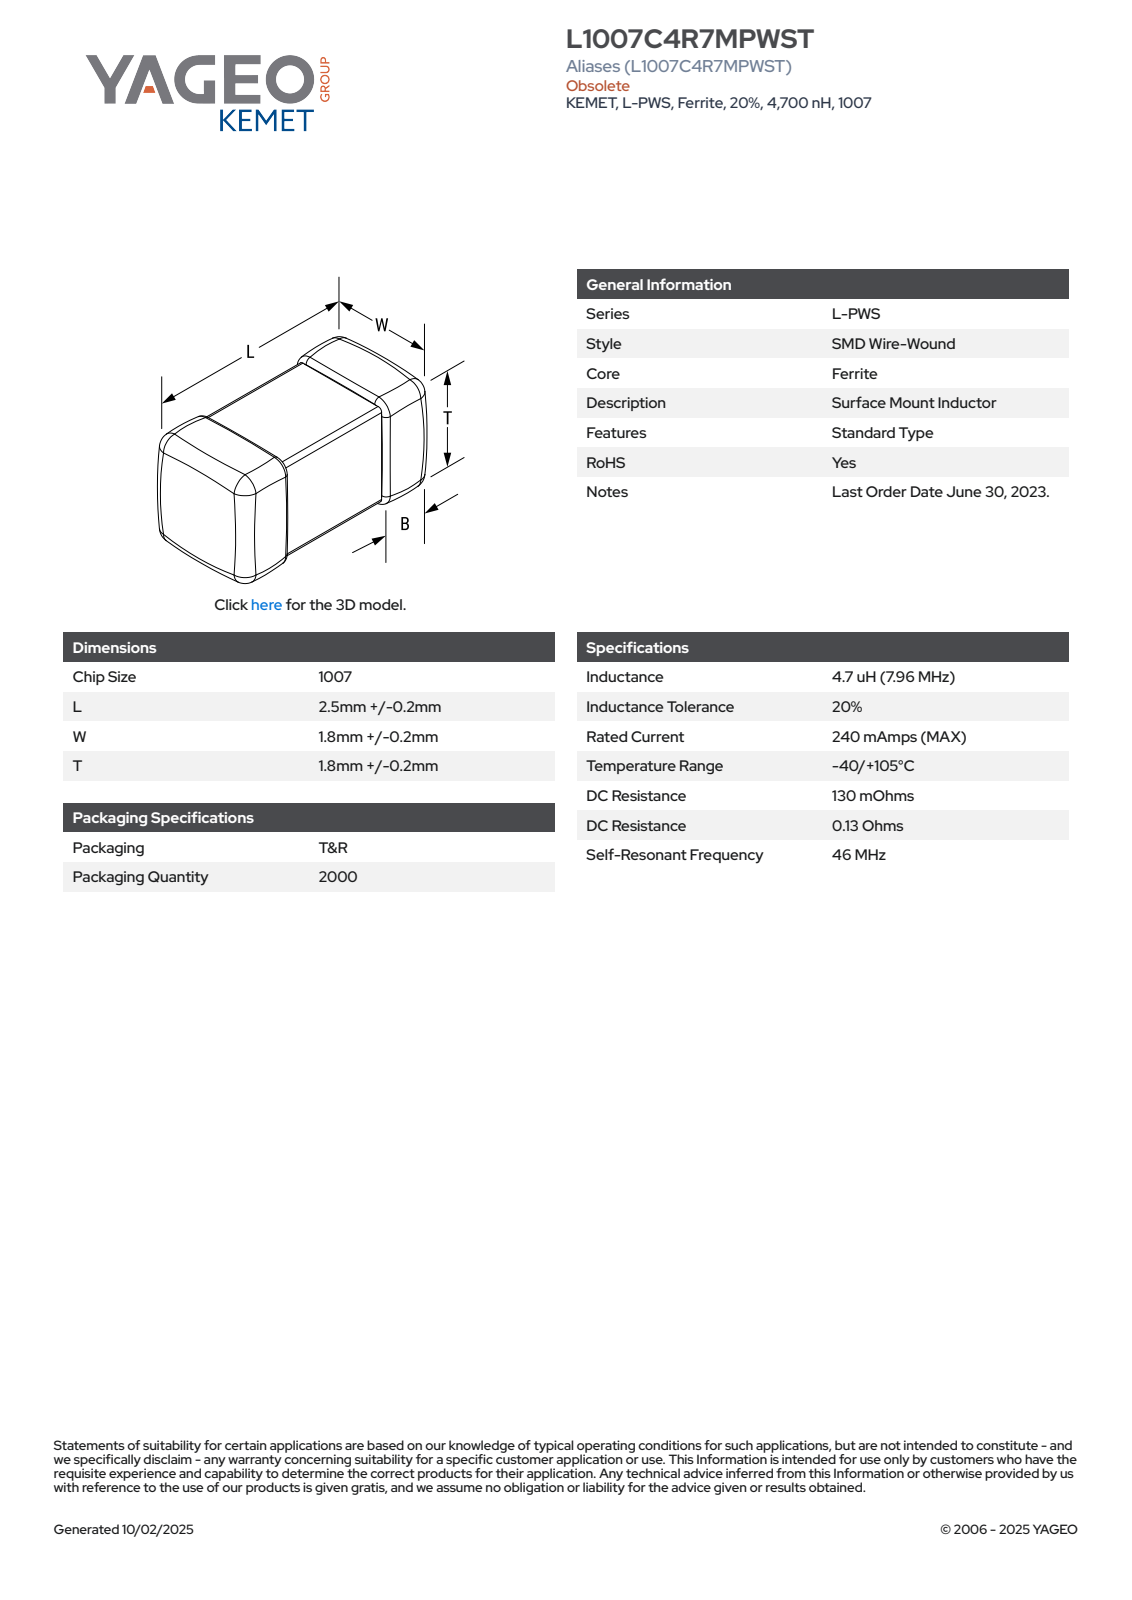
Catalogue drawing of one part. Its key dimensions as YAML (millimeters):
part_name: "IS_KC_1007_L2.7W2T2LL0.7"
step_written_by: "SolidWorks 2014 (AUTOMOTIVE_DESIGN)"
units: millimeters
bodies: {solids: 4, faces: 73, planar: 73, cylindrical: 0, other: 0}
overall_size: [2.7, 2, 2]
volume: 10
surface_area: 30
face_to_face_distances: [1.97, 2, 1.94, 2.7, 0.7, 1.3, 1.19, 0.49, 0.81, 1.51]
